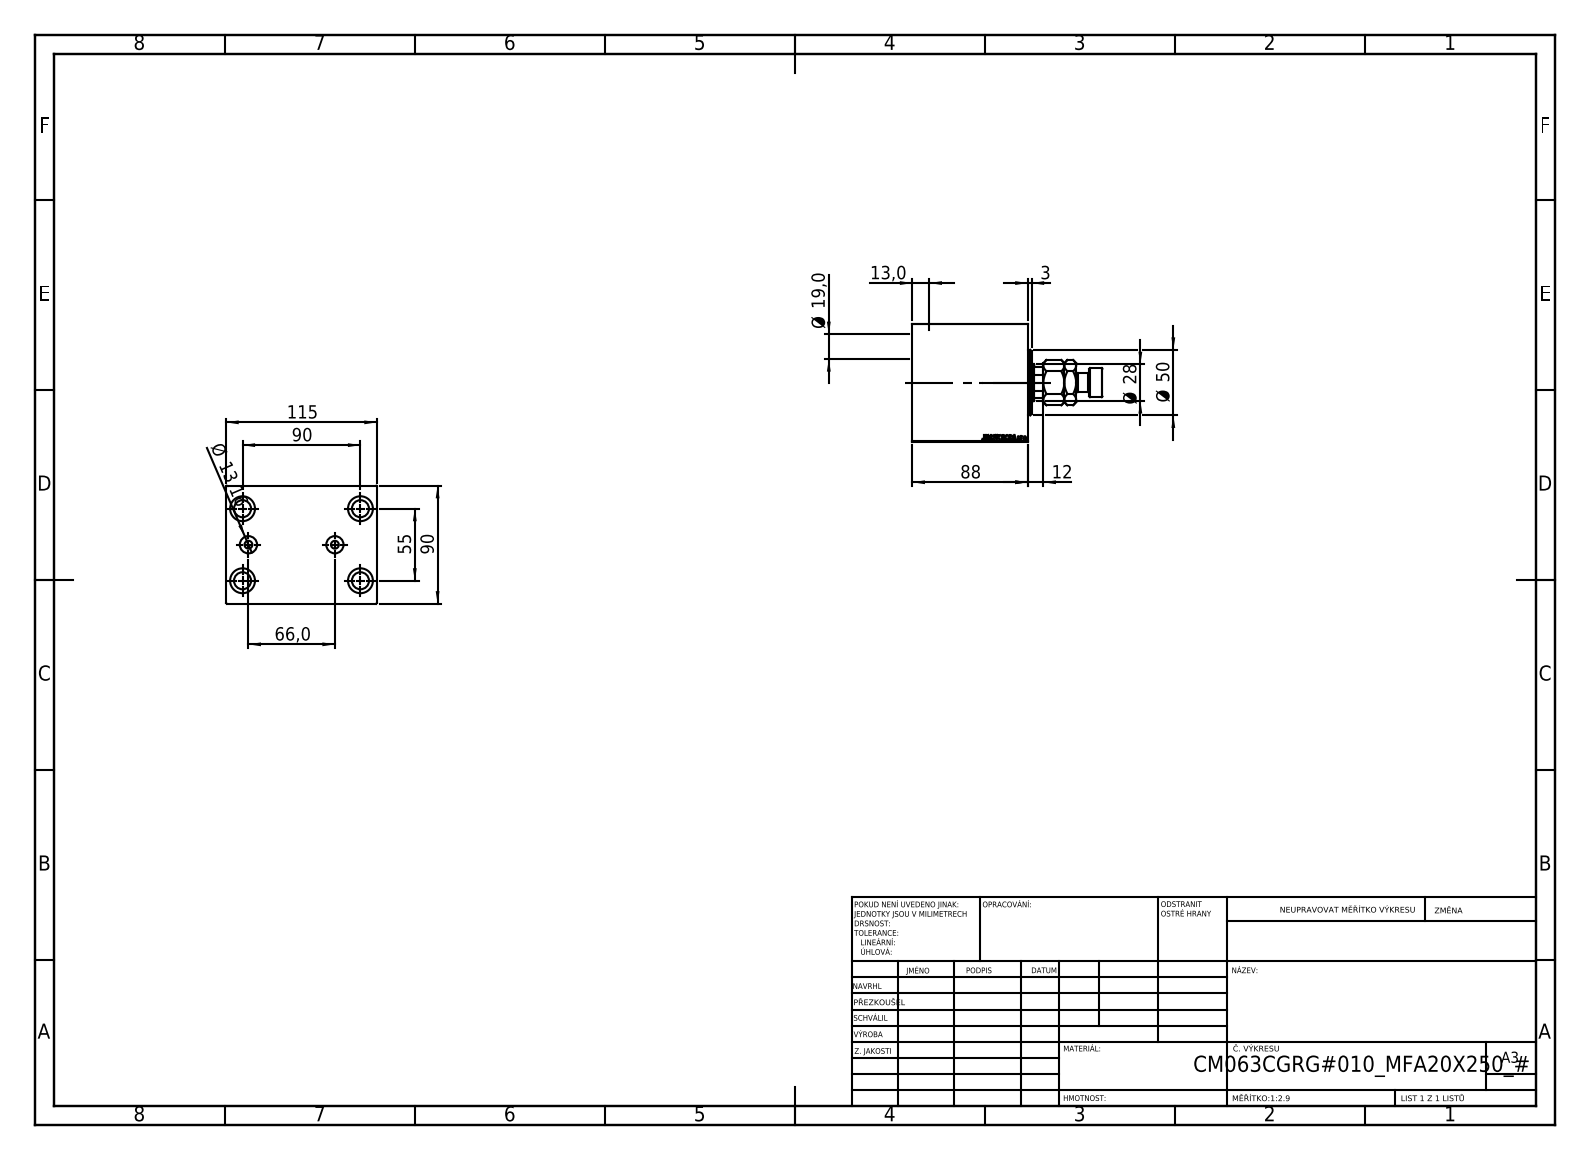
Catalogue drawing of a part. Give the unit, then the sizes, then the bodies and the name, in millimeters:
Units: millimetres
Overall size (bounding box): 145 × 115 × 90
Round holes (diameter × count): ⌀13 ×4, ⌀19 ×4, ⌀6 ×2, ⌀13.16 ×2, ⌀18.5 ×1, ⌀28 ×1, ⌀31.5 ×1, ⌀63 ×1, ⌀65 ×1, ⌀72 ×1
Round bosses / shafts (diameter × count): ⌀50 ×1, ⌀22 ×1, ⌀14 ×1
Partial cylindrical surfaces — rounded edges, fillets, slot ends (radius × count): R13.5 ×1
Main face-to-face distances: 90, 115, 88, 37, 51, 10, 21.6, 29.4, 66.4, 56.4
Hole centre spacings: 52.74, 27.87, 33.71, 55, 75.67, 89.81, 90, 105.48
Volume: 845 510 mm³ · Surface area: 119 874 mm²
Bodies: 4 solids, 912 faces (424 planar, 62 cylindrical, 426 other)
Part name (STEP PRODUCT): V450CM_VC_B; MFA; V450CM_C_Body; V450CM_C_VCP
STEP written by: SolidWorks 2019 (CONFIG_CONTROL_DESIGN)
